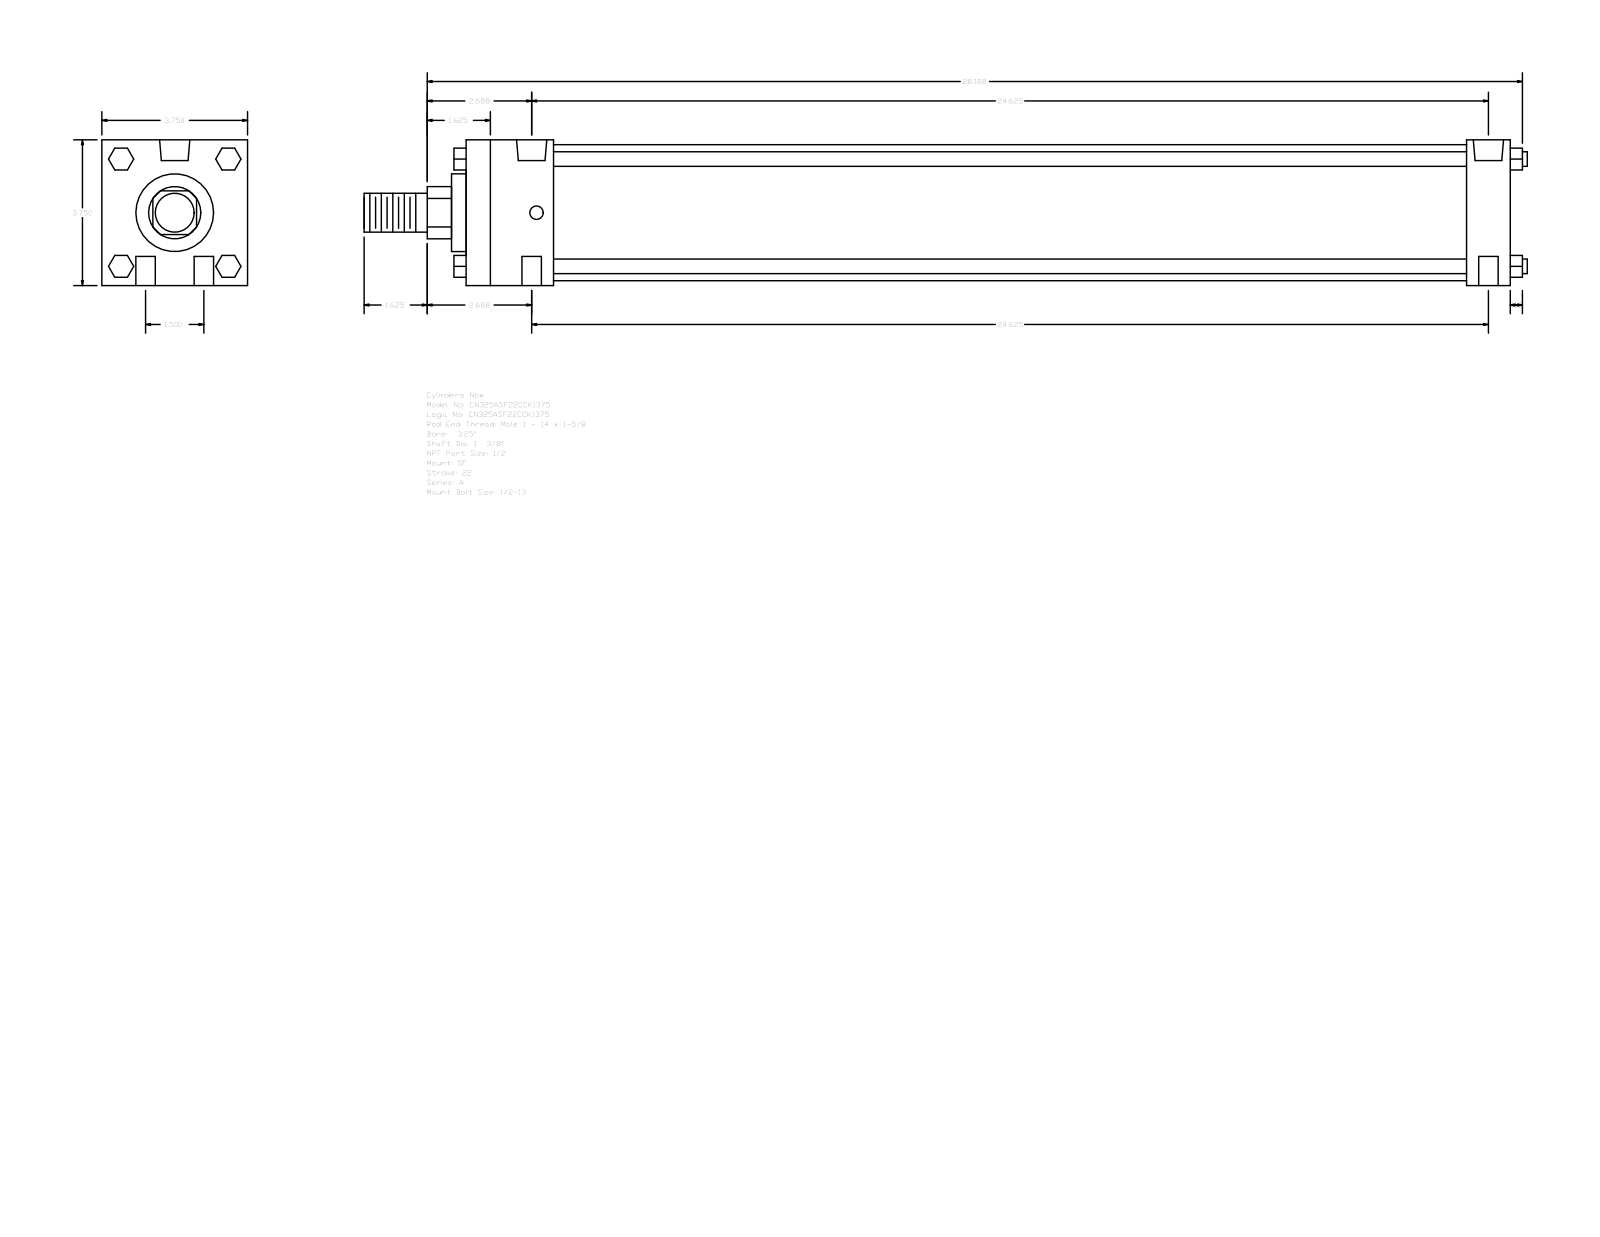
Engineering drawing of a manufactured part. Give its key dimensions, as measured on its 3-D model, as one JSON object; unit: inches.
{"part_name": "A_SF__0325_1.375", "step_written_by": "GSSL Pune (CONFIG_CONTROL_DESIGN)", "units": "inches", "bodies": {"solids": 0, "faces": 124, "planar": 94, "cylindrical": 30, "other": 0}, "overall_size": [29.937, 3.75, 3.75], "round_holes": [[0.5, 4], [0.344, 2], [0.778, 2]], "round_bosses_or_shafts": [[0.375, 4], [3.5, 1], [2, 1], [1.375, 1], [1, 1]], "partial_cylinders_radius": [[0.672, 1]], "face_to_face_distances": [3.75, 26.875, 2.25, 25.75, 1.125, 23.5, 24.625, 2.625, 0.375, 26.125], "hole_center_spacings": [0.75, 24.637, 24.625, 1.5, 24.671, 24.375]}
